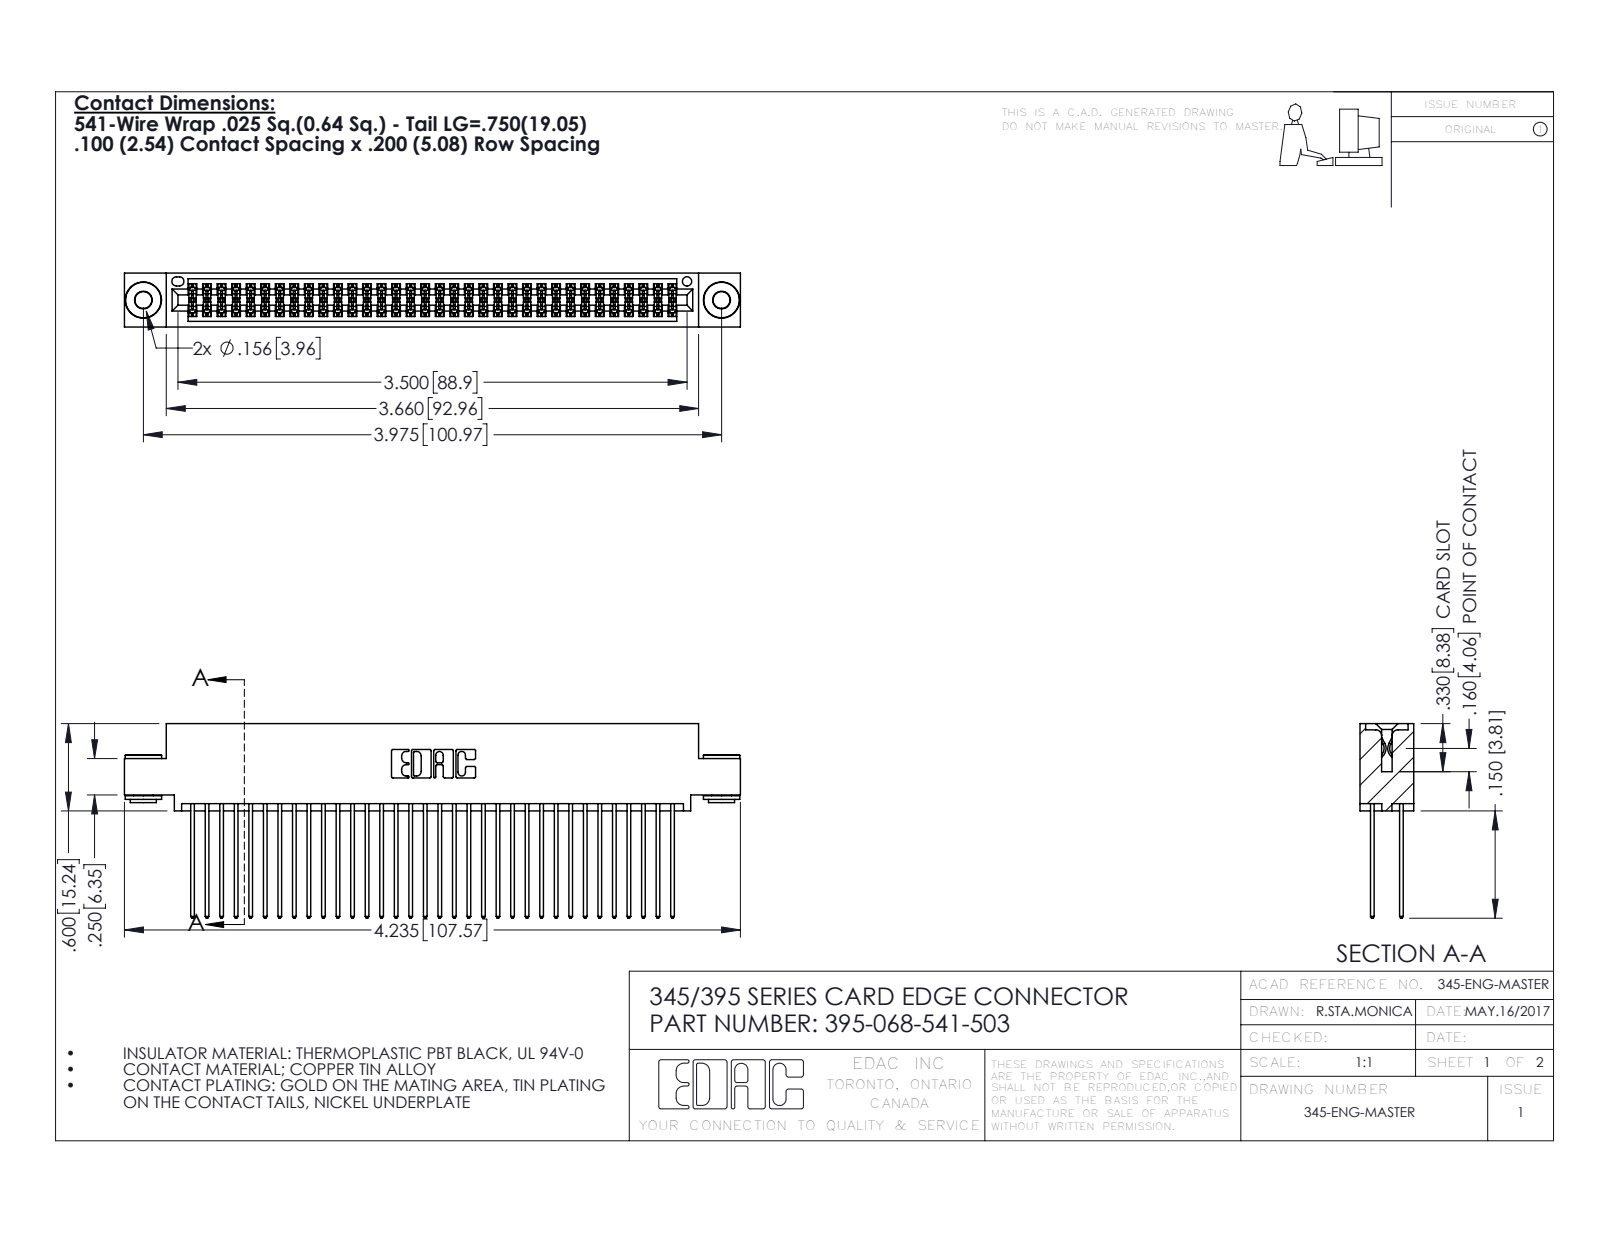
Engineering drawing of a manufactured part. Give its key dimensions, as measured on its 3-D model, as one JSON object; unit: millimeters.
{"part_name": "345-292-001_345-293-141; 345 Part_0.110 Offset - 0.156 Dia-TH; 395-068-541-503; 345-250-002_345-250-002-102", "step_written_by": "SolidWorks 2016 (CONFIG_CONTROL_DESIGN)", "units": "millimeters", "bodies": {"solids": 71, "faces": 3568, "planar": 2338, "cylindrical": 1222, "other": 8}, "overall_size": [107.6, 34, 9.4], "volume_mm3": 10700, "surface_area_mm2": 17810, "round_holes": [[2.9, 2], [4, 2], [1.6, 1]], "round_bosses_or_shafts": [[6.4, 2], [4.6, 2], [3.5, 2]], "partial_cylinders_radius": [[0.2, 102], [0.3, 68], [0.3, 22], [0.2, 6], [0.8, 6], [0.7, 3], [0.4, 2], [0.5, 2]], "face_to_face_distances": [1.8, 7.6, 5.1, 0.6, 2.5, 6.9, 5.7, 9.4, 4.4, 3.8], "hole_center_spacings": [6.9, 95, 101]}
